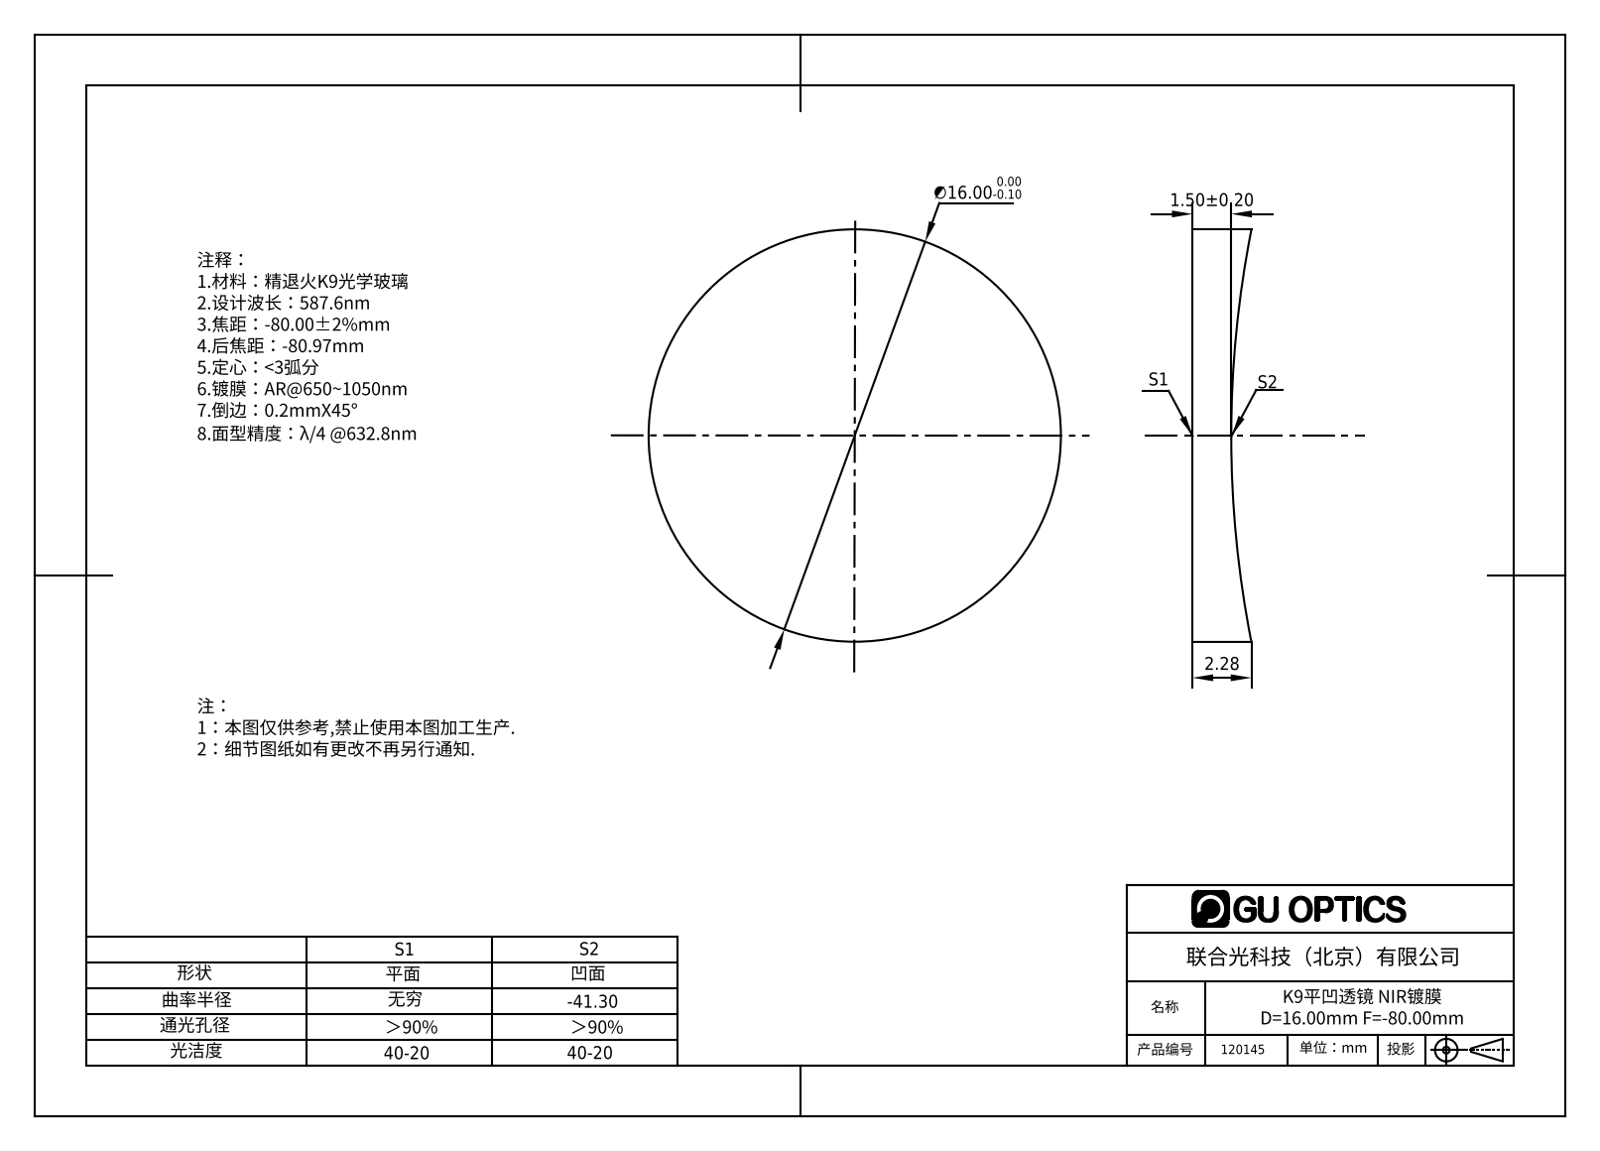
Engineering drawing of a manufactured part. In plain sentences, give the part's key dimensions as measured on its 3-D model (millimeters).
The part is named "120145". Its 3-D file was written by "SolidWorks 2016 (AUTOMOTIVE_DESIGN)". It is 1 solid with 5 faces: 1 planar, 2 cylindrical and 2 other. Overall it measures 16 by 16 by 2.28 millimeters. Its volume is 380 cubic millimeters and its surface area 519 square millimeters. Round bosses or shafts: 1 of diameter 16.
